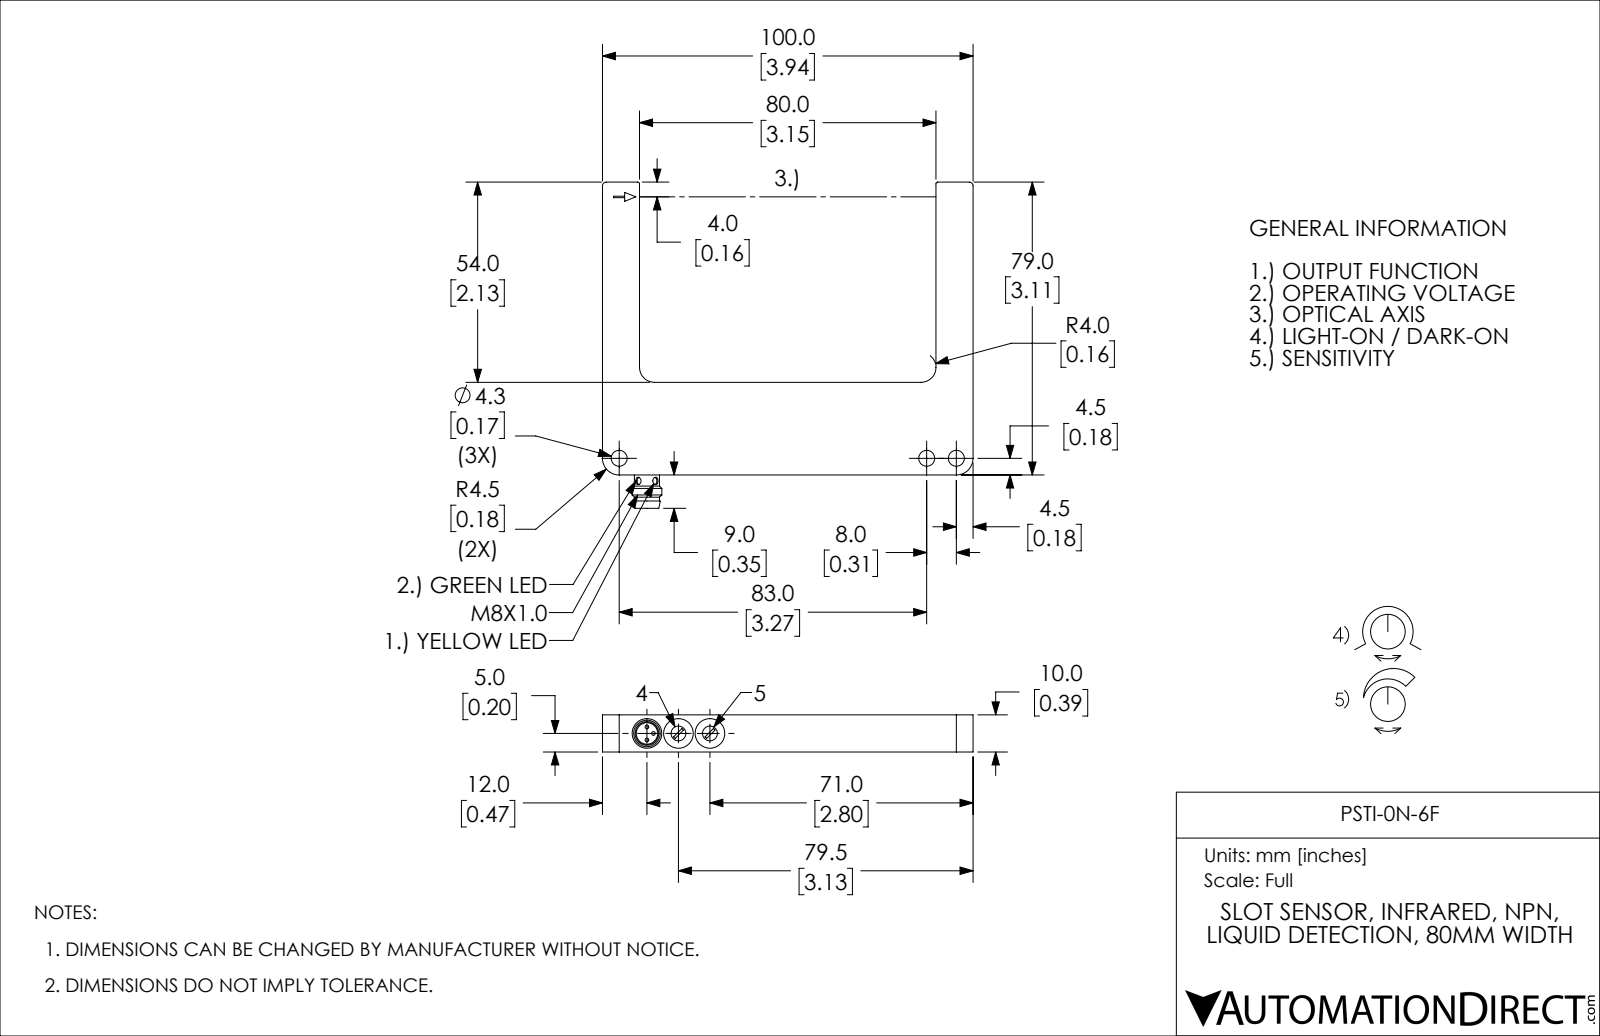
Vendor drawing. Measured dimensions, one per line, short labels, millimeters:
name: PSTI-0N-6F
written by: SolidWorks 2017 (AUTOMOTIVE_DESIGN)
unit: mm
bodies: 1 solid, 71 faces (35 planar, 30 cylindrical, 6 other)
size: 100 × 88 × 10
volume: 35 560 mm³; area: 12 420 mm²
holes: 3× ⌀4.3, 2× ⌀2, 2× ⌀4, 2× ⌀8, 1× ⌀5.8
bosses: 3× ⌀1, 1× ⌀8, 1× ⌀6.8
rounds: 2× R0.5, 2× R1, 2× R1.6, 2× R4, 2× R4.5
face distances: 10, 90, 100, 25, 80, 54, 79, 78.9, 24.9, 4
hole spacings: 8.5, 8, 17, 83, 91
